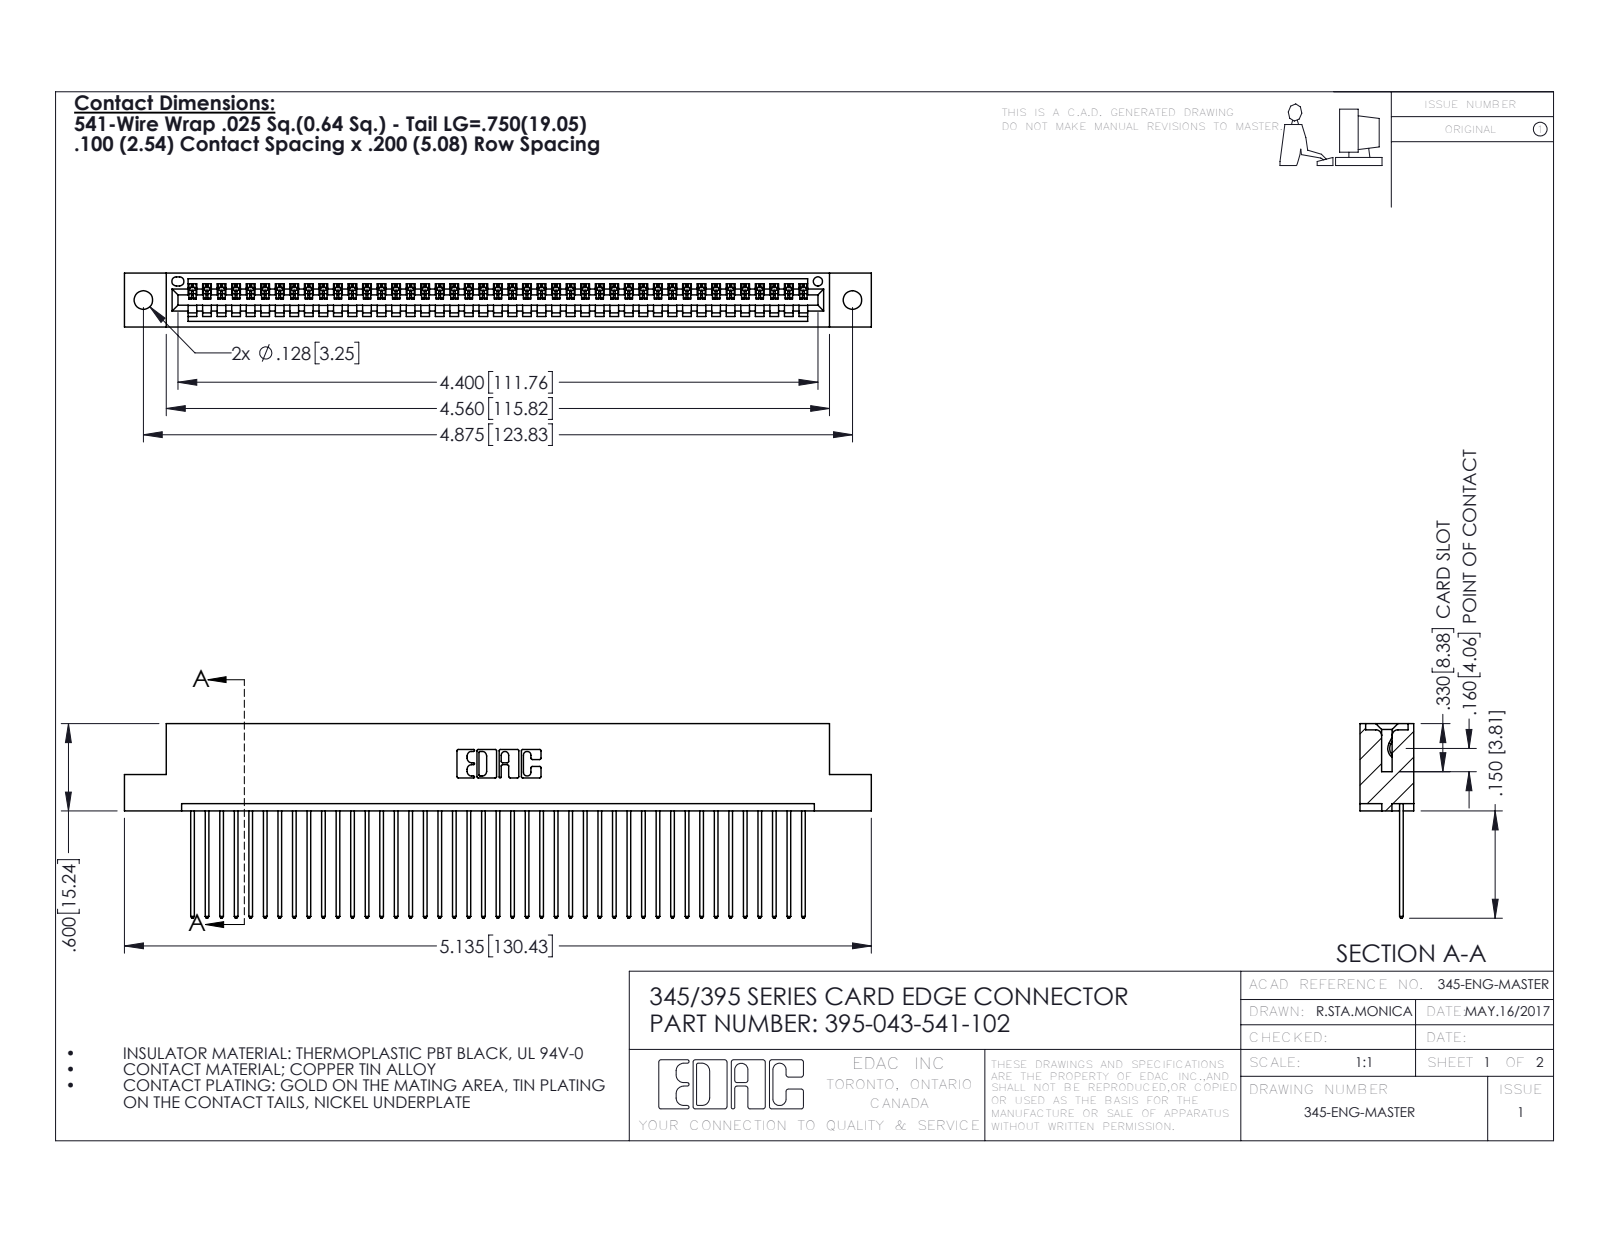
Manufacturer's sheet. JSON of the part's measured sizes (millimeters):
{"part_name": "345 Part_Flush Mounting Lugs - 0.128 Dia; 345-292-001_345-293-141; 395-043-541-102", "step_written_by": "SolidWorks 2016 (CONFIG_CONTROL_DESIGN)", "units": "millimeters", "bodies": {"solids": 44, "faces": 2620, "planar": 1800, "cylindrical": 820, "other": 0}, "overall_size": [130.4, 34, 9.4], "volume_mm3": 12500, "surface_area_mm2": 17190, "round_holes": [[3.3, 2], [1.6, 1]], "partial_cylinders_radius": [[0.2, 86], [0.3, 86], [0.3, 22], [0.2, 6], [0.8, 6], [0.7, 3], [0.8, 2], [1, 2]], "face_to_face_distances": [1.8, 7.6, 2.5, 6.9, 0.6, 9.4, 5.1, 5.7, 3.8, 1.8], "hole_center_spacings": [6.9, 117.8, 123.8]}
